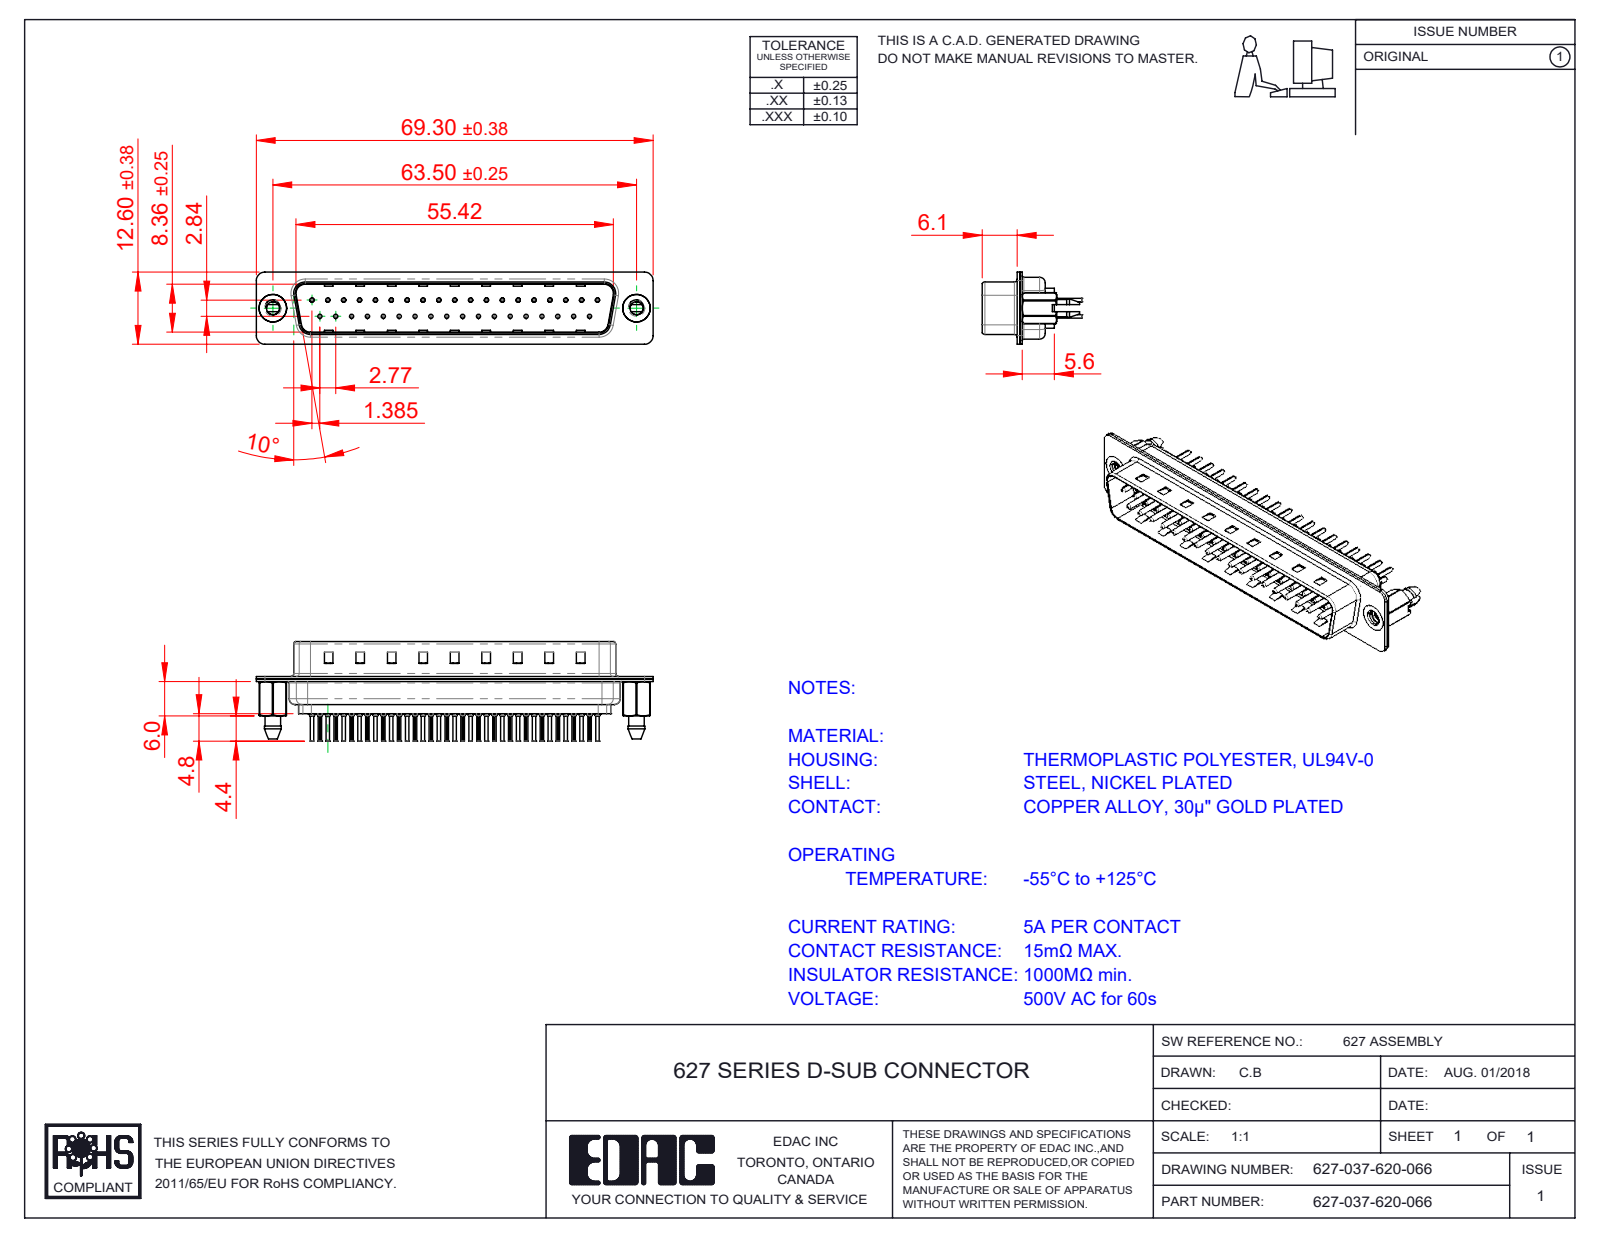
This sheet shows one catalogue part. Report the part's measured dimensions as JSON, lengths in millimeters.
{"part_name": "627 Shell Rear_37 Contacts; 627 Shell Front_37 Contacts; 627 Contact Row 1_20L; 627 4-40 Threaded Boardlock_LP (+3 more)", "step_written_by": "SolidWorks 2020 (CONFIG_CONTROL_DESIGN)", "units": "millimeters", "bodies": {"solids": 42, "faces": 4112, "planar": 1123, "cylindrical": 1542, "other": 1447}, "overall_size": [69.3, 17.3, 12.6], "volume_mm3": 3816, "surface_area_mm2": 10972, "round_holes": [[0.2, 37], [0.35, 37], [1.1, 37], [1.6, 37], [2.26, 2], [4, 2], [4.8, 2]], "round_bosses_or_shafts": [[2, 37], [1.5, 37], [0.75, 37], [0.6, 37], [4.9, 2]], "partial_cylinders_radius": [[0.1, 74], [1.5, 18], [2, 12], [1.6, 10], [0.5, 8], [0.25, 4], [0.6, 4], [0.65, 4]], "face_to_face_distances": [0.4, 0.82, 9.58, 0.45, 8.76, 1.5, 0.9, 1.4, 6.5, 6.05], "hole_center_spacings": [3.16, 2.77, 5.54, 8.31, 5.04, 10.1, 11.08, 12.78]}
